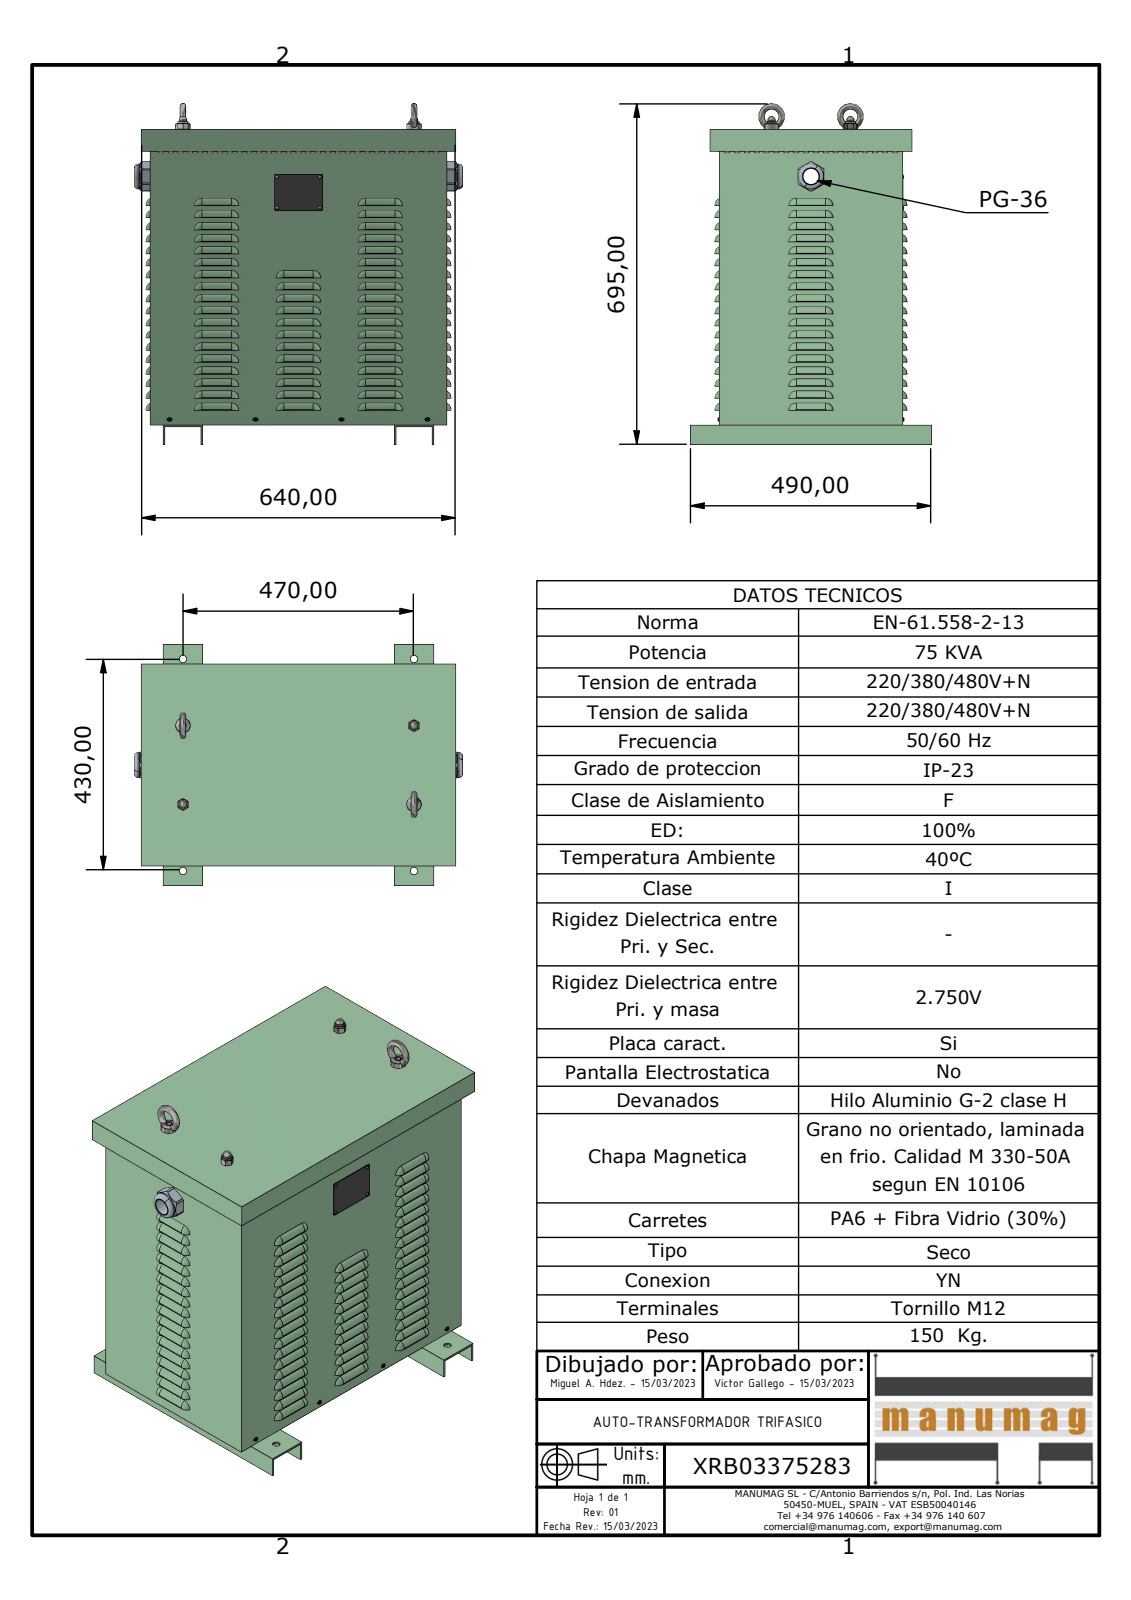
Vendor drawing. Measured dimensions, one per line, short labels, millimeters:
name: XRB03375283; JE060 - JE075 CUERPO; JE060 - JE075 BASE; JE060 - JE075 PATAS (+7 more)
written by: Autodesk Inventor 2023 (AUTOMOTIVE_DESIGN)
unit: mm
bodies: 24 solids, 2907 faces (1145 planar, 1024 cylindrical, 738 other)
size: 695 × 668.2 × 490
volume: 4 615 000 mm³; area: 4 047 000 mm²
holes: 364× ⌀11, 8× ⌀15, 4× ⌀4, 4× ⌀5, 2× ⌀10.11, 2× ⌀11.84, 1× ⌀32, 1× ⌀48
bosses: 4× ⌀4, 4× ⌀3.62, 4× ⌀3.2, 2× ⌀51.1, 2× ⌀30, 2× ⌀21, 2× ⌀15.6, 1× ⌀47.45
rounds: 132× R14, 72× R7, 72× R15, 12× R3.88, 8× R2.5, 4× R2, 4× R7.5, 2× R30
face distances: 2, 370, 600, 601, 368, 372, 602, 599, 598, 603
hole spacings: 30, 21.21, 128.88, 132, 147, 173.76, 279, 117
